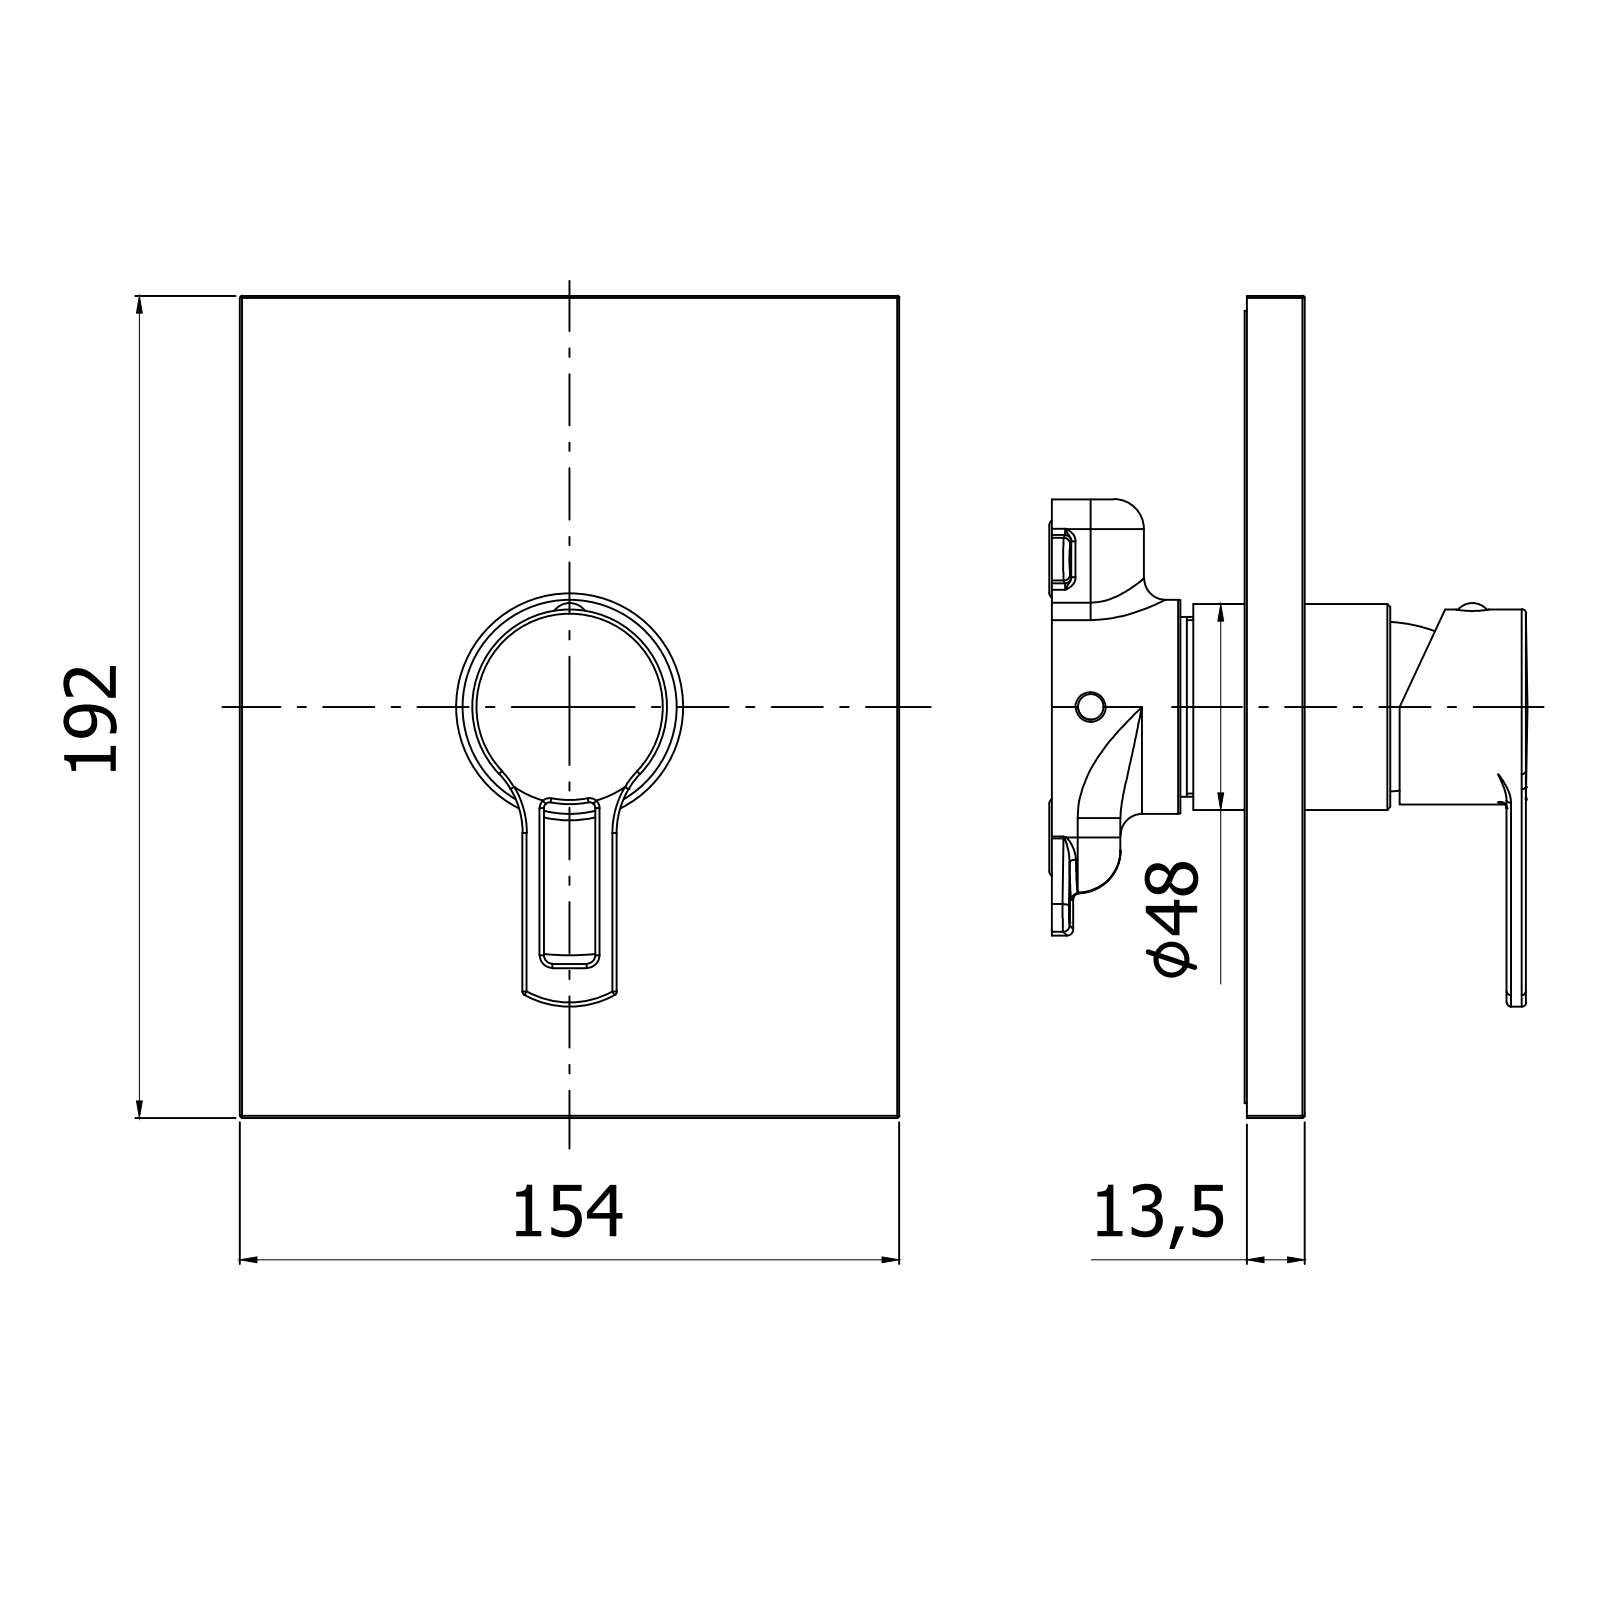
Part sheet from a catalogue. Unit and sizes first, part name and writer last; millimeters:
Units: millimetres
Overall size (bounding box): 192 × 154 × 65.6
Round holes (diameter × count): ⌀5 ×3, ⌀7 ×3, ⌀2 ×2, ⌀4 ×2, ⌀3 ×1, ⌀3.3 ×1, ⌀7.8 ×1, ⌀19.5 ×1, ⌀19.9 ×1, ⌀26.8 ×1, ⌀29 ×1, ⌀31 ×1
Round bosses / shafts (diameter × count): ⌀4.8 ×2, ⌀57 ×1, ⌀48.1 ×1, ⌀44.8 ×1, ⌀39 ×1, ⌀35 ×1, ⌀34.8 ×1, ⌀32.2 ×1
Partial cylindrical surfaces — rounded edges, fillets, slot ends (radius × count): R0.5 ×43, R1 ×14, R0.15 ×11, R0.3 ×4, R2 ×4, R20 ×2, R2.5 ×1, R7 ×1
Main face-to-face distances: 13.5, 10.5, 3, 23.5, 130.5, 3.5, 154, 168.5, 192, 65.6
Hole centre spacings: 8.6, 13.45, 15.13, 21.93, 11, 14, 18
Volume: 296 231 mm³ · Surface area: 118 835 mm²
Bodies: 2 solids, 1123 faces (634 planar, 277 cylindrical, 212 other)
Part name (STEP PRODUCT): RINBOX010CR
STEP written by: CREO PARAMETRIC BY PTC INC, 2020044 (CONFIG_CONTROL_DESIGN)
